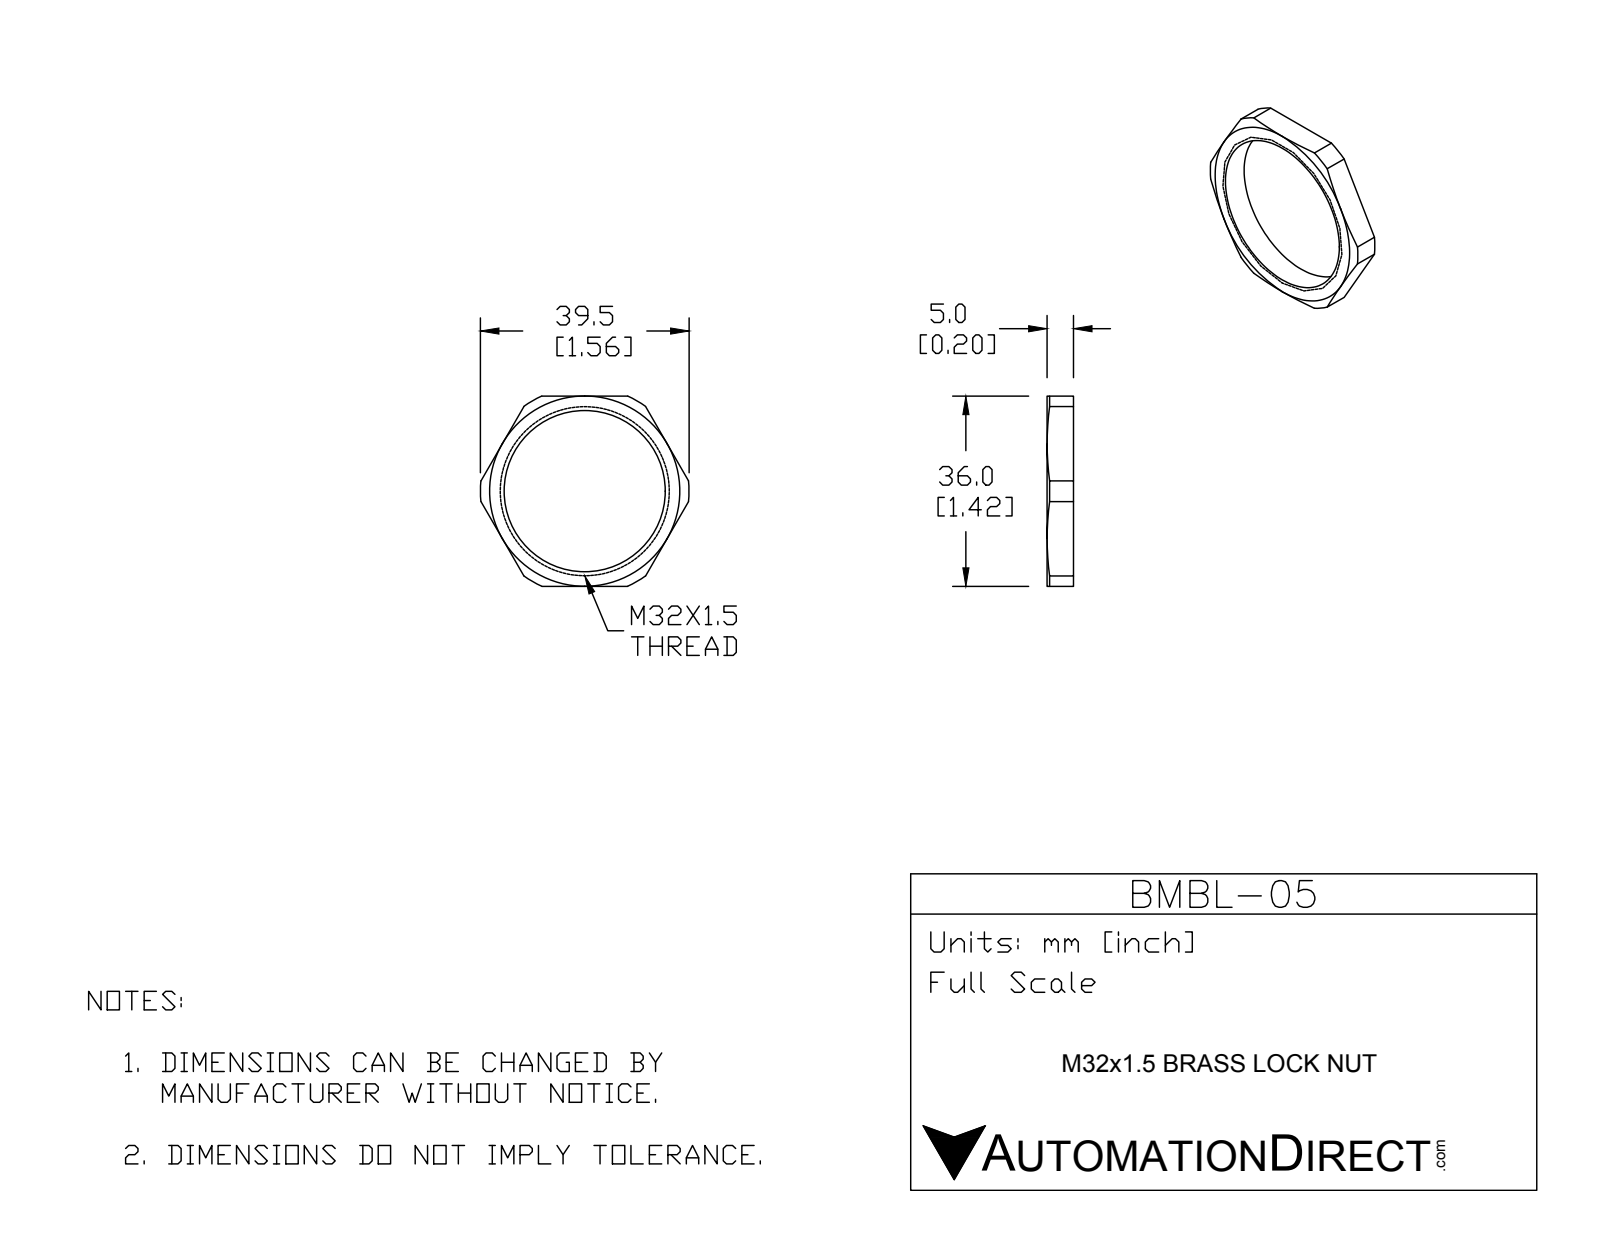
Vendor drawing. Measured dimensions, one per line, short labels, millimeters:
name: BMBL-05
written by: SolidWorks 2015 (CONFIG_CONTROL_DESIGN)
unit: mm
bodies: 1 solid, 23 faces (8 planar, 9 cylindrical, 6 other)
size: 39.5 × 36 × 5
volume: 1 883 mm³; area: 1 821 mm²
holes: 1× ⌀30.5
rounds: 1× R19.75
face distances: 5, 36
